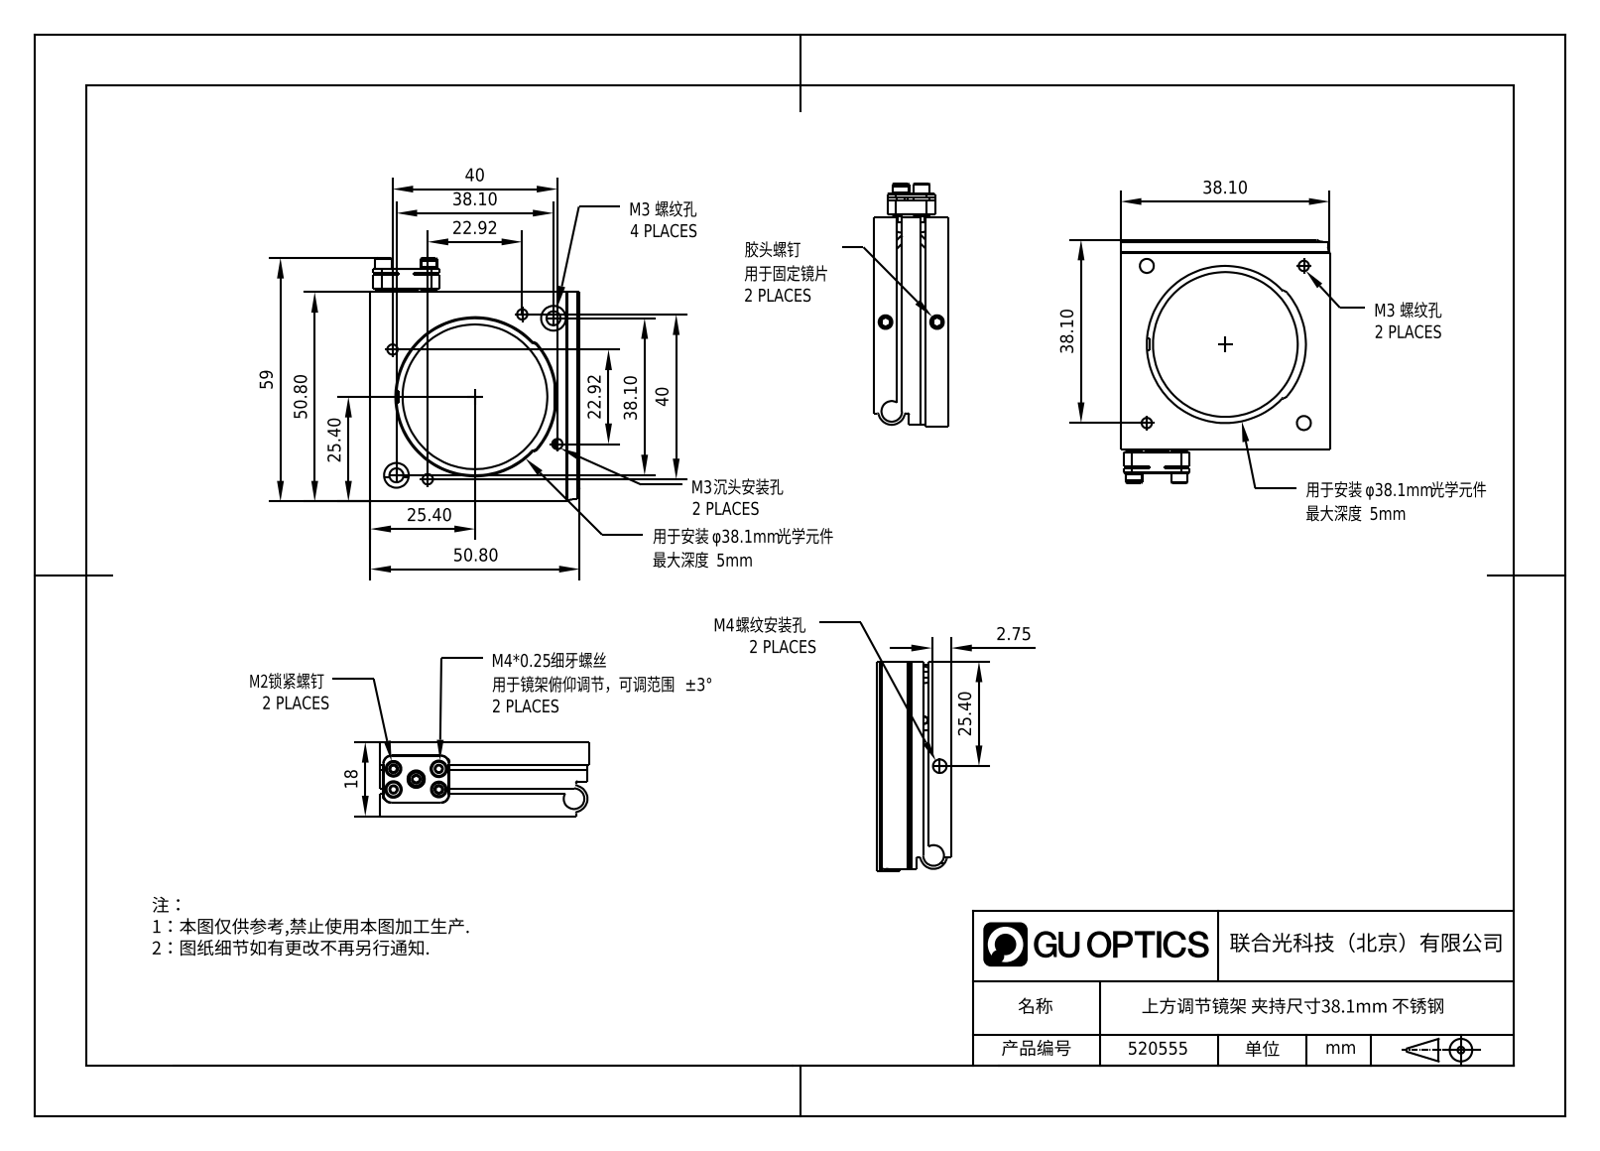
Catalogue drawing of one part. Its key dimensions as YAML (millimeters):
part_name: "1.1.6.23_ZJR-BS1.5"
step_written_by: "SolidWorks 2021 (CONFIG_CONTROL_DESIGN)"
units: millimeters
bodies: {solids: 0, faces: 270, planar: 96, cylindrical: 114, other: 60}
overall_size: [59.09, 50.8, 18]
round_holes:
  - {diameter: 2.5, count: 6}
  - {diameter: 3.3, count: 3}
  - {diameter: 3.4, count: 2}
  - {diameter: 5, count: 2}
  - {diameter: 6, count: 2}
  - {diameter: 1.5, count: 1}
  - {diameter: 4, count: 1}
  - {diameter: 35.1, count: 1}
round_bosses_or_shafts:
  - {diameter: 1.5, count: 3}
  - {diameter: 4, count: 2}
  - {diameter: 3.8, count: 2}
  - {diameter: 3, count: 1}
partial_cylinders:
  - {radius: 0.35, count: 6}
  - {radius: 2, count: 5}
  - {radius: 1.5, count: 4}
  - {radius: 0.5, count: 2}
  - {radius: 0.75, count: 2}
  - {radius: 2.25, count: 2}
  - {radius: 2.5, count: 2}
  - {radius: 3.25, count: 2}
face_to_face_distances: [5.75, 1.25, 6.75, 11.25, 5.5, 12.5, 4.5, 7, 18, 0.5]
hole_center_spacings: [7.65, 23.05, 26.94, 30.52, 32.6, 38.1, 39.78, 49.56]
